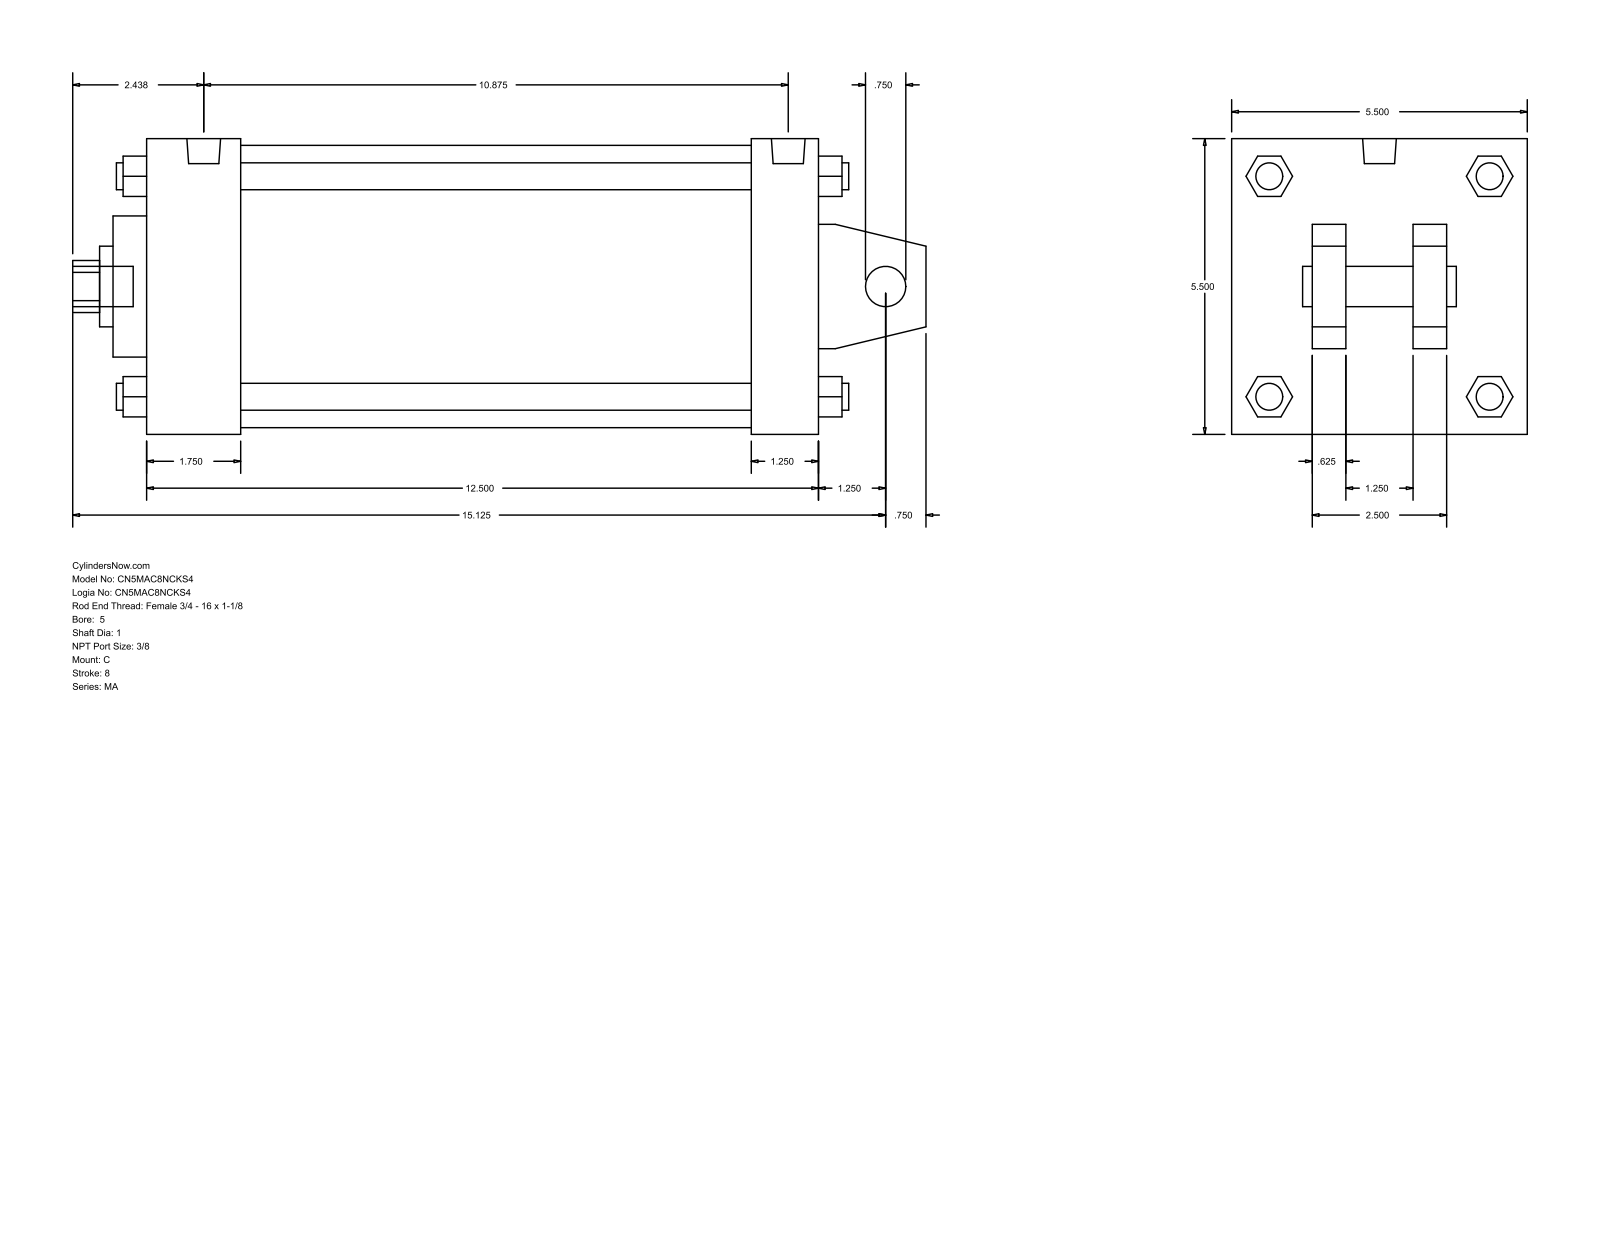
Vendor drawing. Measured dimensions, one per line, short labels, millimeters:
name: MA_C__0500_1
written by: GSSL Pune (CONFIG_CONTROL_DESIGN)
unit: mm
bodies: 0 solids, 141 faces (109 planar, 32 cylindrical, 0 other)
size: 403.23 × 139.7 × 139.7
holes: 1× ⌀19.05, 1× ⌀25.4, 1× ⌀38.1, 1× ⌀66.67, 1× ⌀133.35
bosses: 4× ⌀12.7, 4× ⌀11.11, 2× ⌀15.93, 1× ⌀19.05
rounds: 1× R12.29
face distances: 139.7, 317.51, 15.87, 285.76, 31.75, 44.46, 241.3, 273.05, 38.1, 101.6
